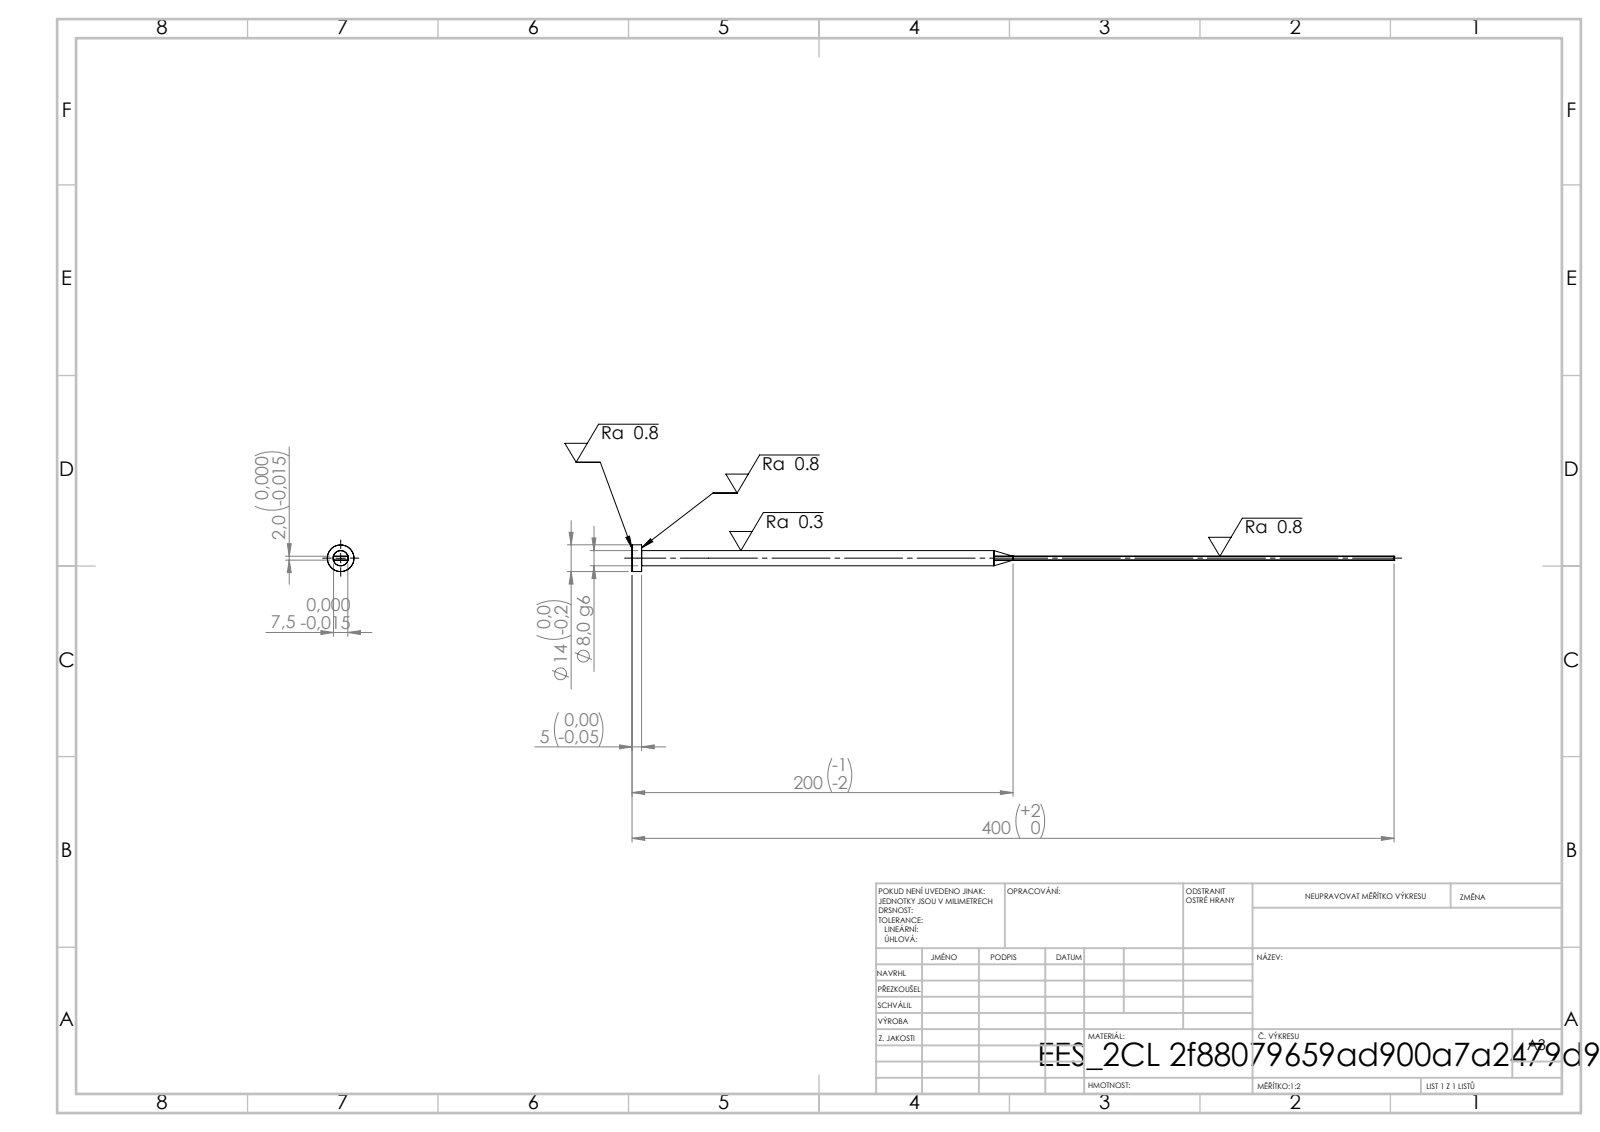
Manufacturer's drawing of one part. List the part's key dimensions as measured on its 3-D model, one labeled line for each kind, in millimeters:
STEP written by: SolidWorks 2019 (CONFIG_CONTROL_DESIGN)
Units: millimetres
Bodies: 1 solid, 15 faces (7 planar, 4 cylindrical, 4 other)
Overall size (bounding box): 400 × 14 × 14
Volume: 13 383 mm³ · Surface area: 9 158 mm²
Round bosses / shafts (diameter × count): ⌀14 ×1, ⌀8 ×1
Main face-to-face distances: 2, 7.5, 5, 400, 395
